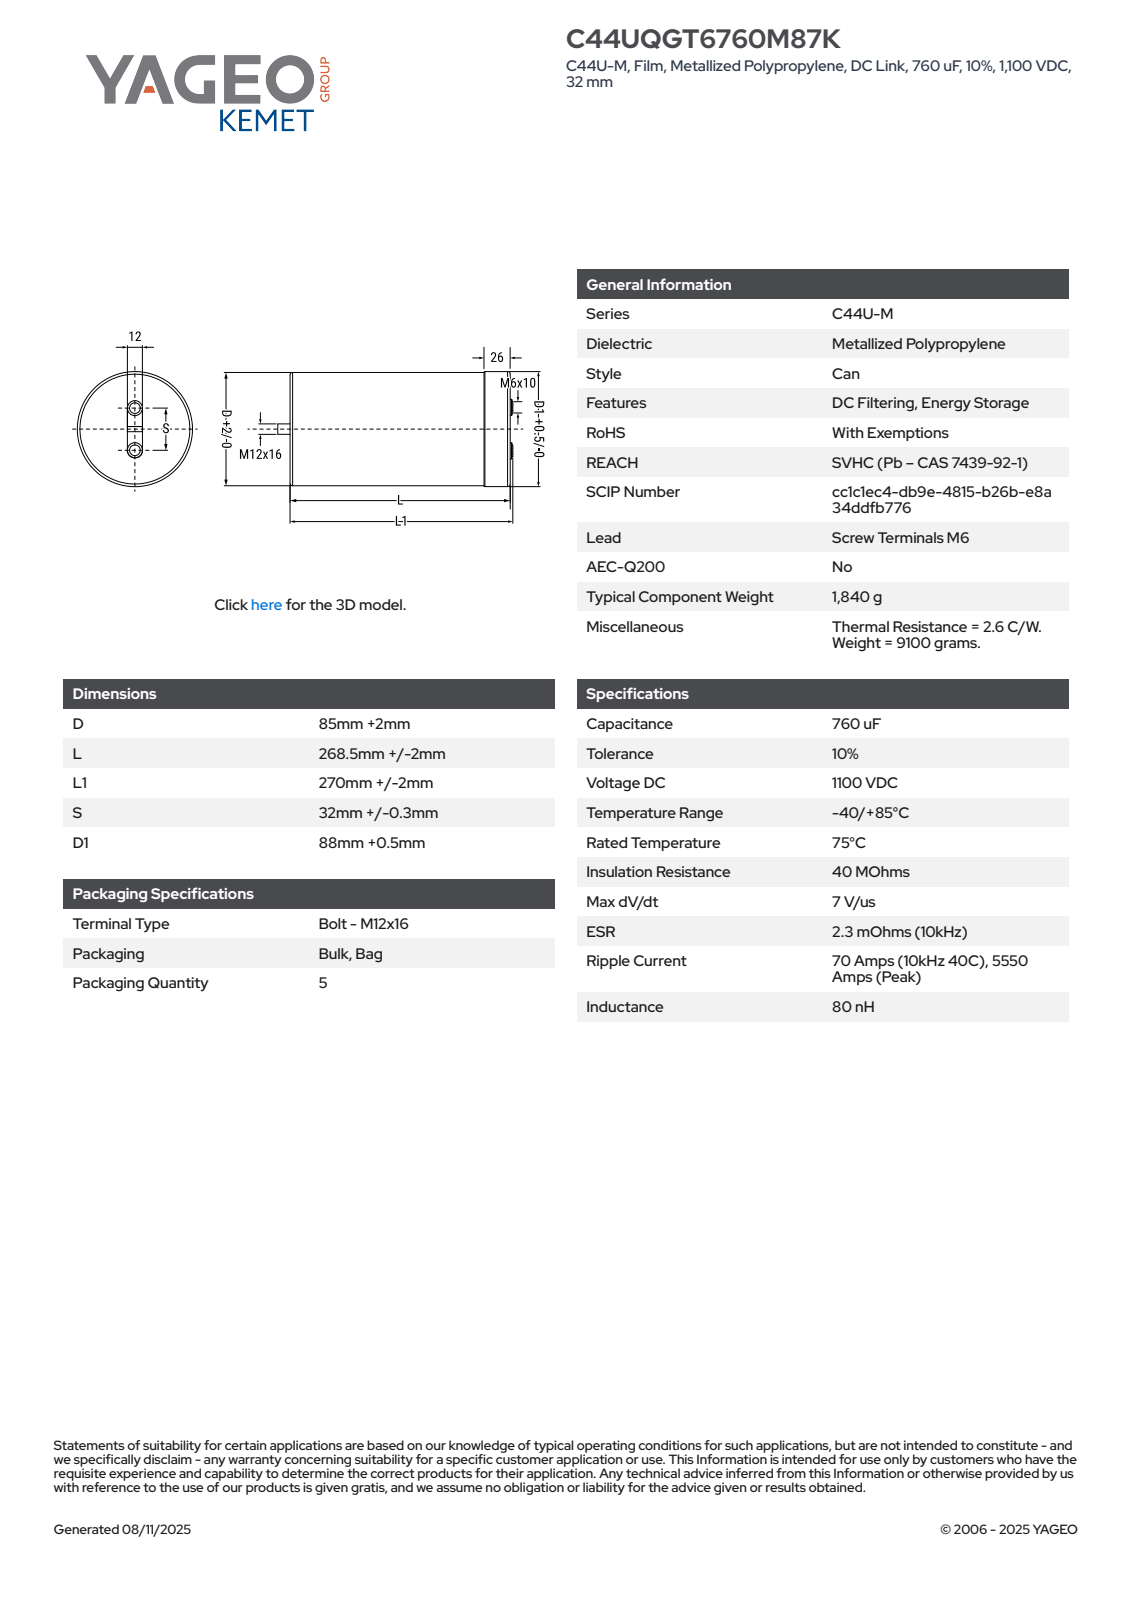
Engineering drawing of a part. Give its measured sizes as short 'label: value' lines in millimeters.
name: CFP_C44UMR_85X268.5_D87L270.5S32L1272D188.5
written by: SolidWorks 2014 (AUTOMOTIVE_DESIGN)
unit: mm
bodies: 1 solid, 84 faces (32 planar, 21 cylindrical, 31 other)
size: 288 × 88.5 × 88.5
volume: 1 615 000 mm³; area: 87 451 mm²
holes: 2× ⌀6
bosses: 3× ⌀12, 2× ⌀10, 1× ⌀88.5, 1× ⌀87
rounds: 1× R43.51
face distances: 270.5, 244.5, 26, 16, 260.5, 286.5, 288, 272, 27.5, 1.5
hole spacings: 32
